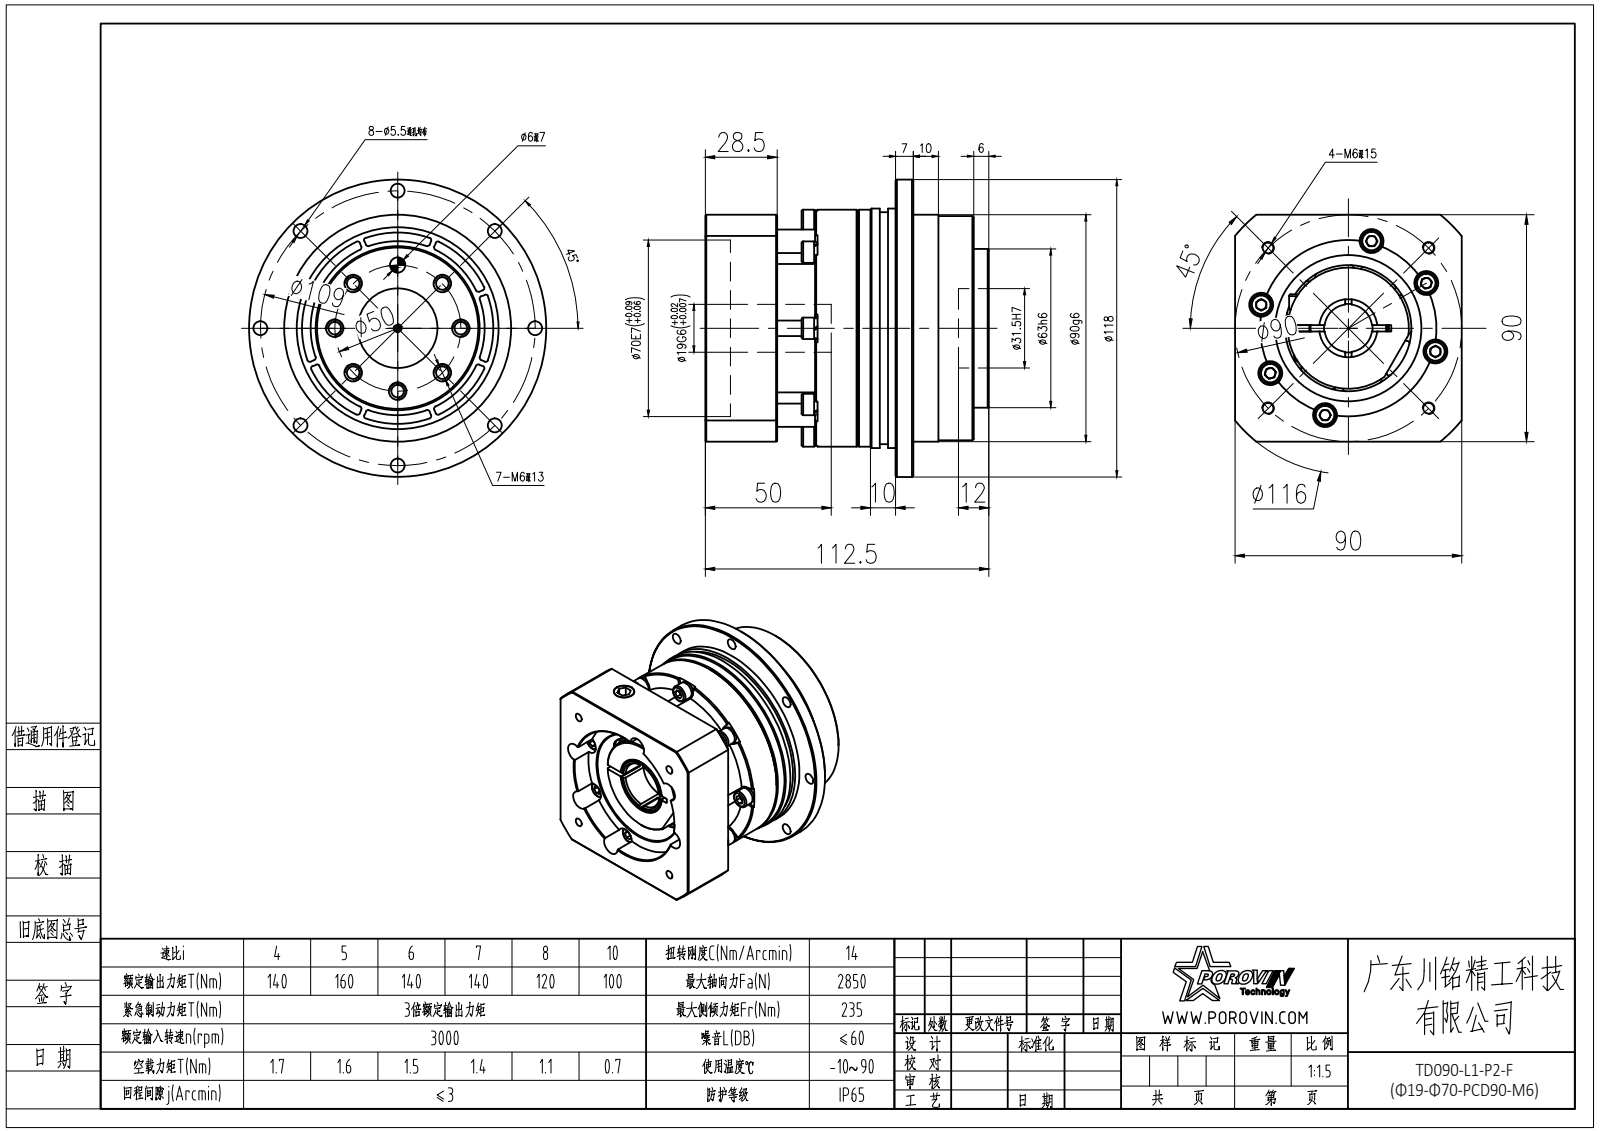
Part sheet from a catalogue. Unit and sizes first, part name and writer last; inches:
Units: inches
Overall size (bounding box): 4.646 × 4.646 × 4.429
Round holes (diameter × count): ⌀0.217 ×22, ⌀0.213 ×14, ⌀0.197 ×12, ⌀0.276 ×7, ⌀0.165 ×6, ⌀0.374 ×6, ⌀0.236 ×1, ⌀0.256 ×1, ⌀0.402 ×1, ⌀0.748 ×1, ⌀0.756 ×1, ⌀1.24 ×1
Round bosses / shafts (diameter × count): ⌀0.315 ×14, ⌀0.335 ×9, ⌀0.197 ×9, ⌀0.394 ×6, ⌀0.236 ×6, ⌀4.646 ×1, ⌀3.74 ×1, ⌀3.701 ×1
Partial cylindrical surfaces — rounded edges, fillets, slot ends (radius × count): R0.039 ×32, R0.187 ×8, R0.217 ×1, R1.378 ×1, R2.283 ×1
Main face-to-face distances: 1.22, 1.85, 0.394, 1.26, 0.866, 0.63, 0.591, 0.098, 1.024, 1.457
Hole centre spacings: 2.926, 1.208, 1.526, 2.479, 2.727, 3.542, 0.754, 0.984
Volume: 37.75 in³ · Surface area: 214.1 in²
Bodies: 36 solids, 1087 faces (447 planar, 416 cylindrical, 224 other)
Part name (STEP PRODUCT): hex socket set screws with flat point gb_GB_FASTENER_SCREWS_HSFP M12X12-N; spring lock washers--normal type gb_GB_FASTENER_WASHER_SW 5; hexagon socket head cap screws gb_GB_FASTENER_SCREWS_HSHCS M6X20-N; hexagon socket head cap screws gb_GB_FASTENER_SCREWS_HSHCS M5X20-N (+1 more)
STEP written by: SolidWorks 2016 (CONFIG_CONTROL_DESIGN)
